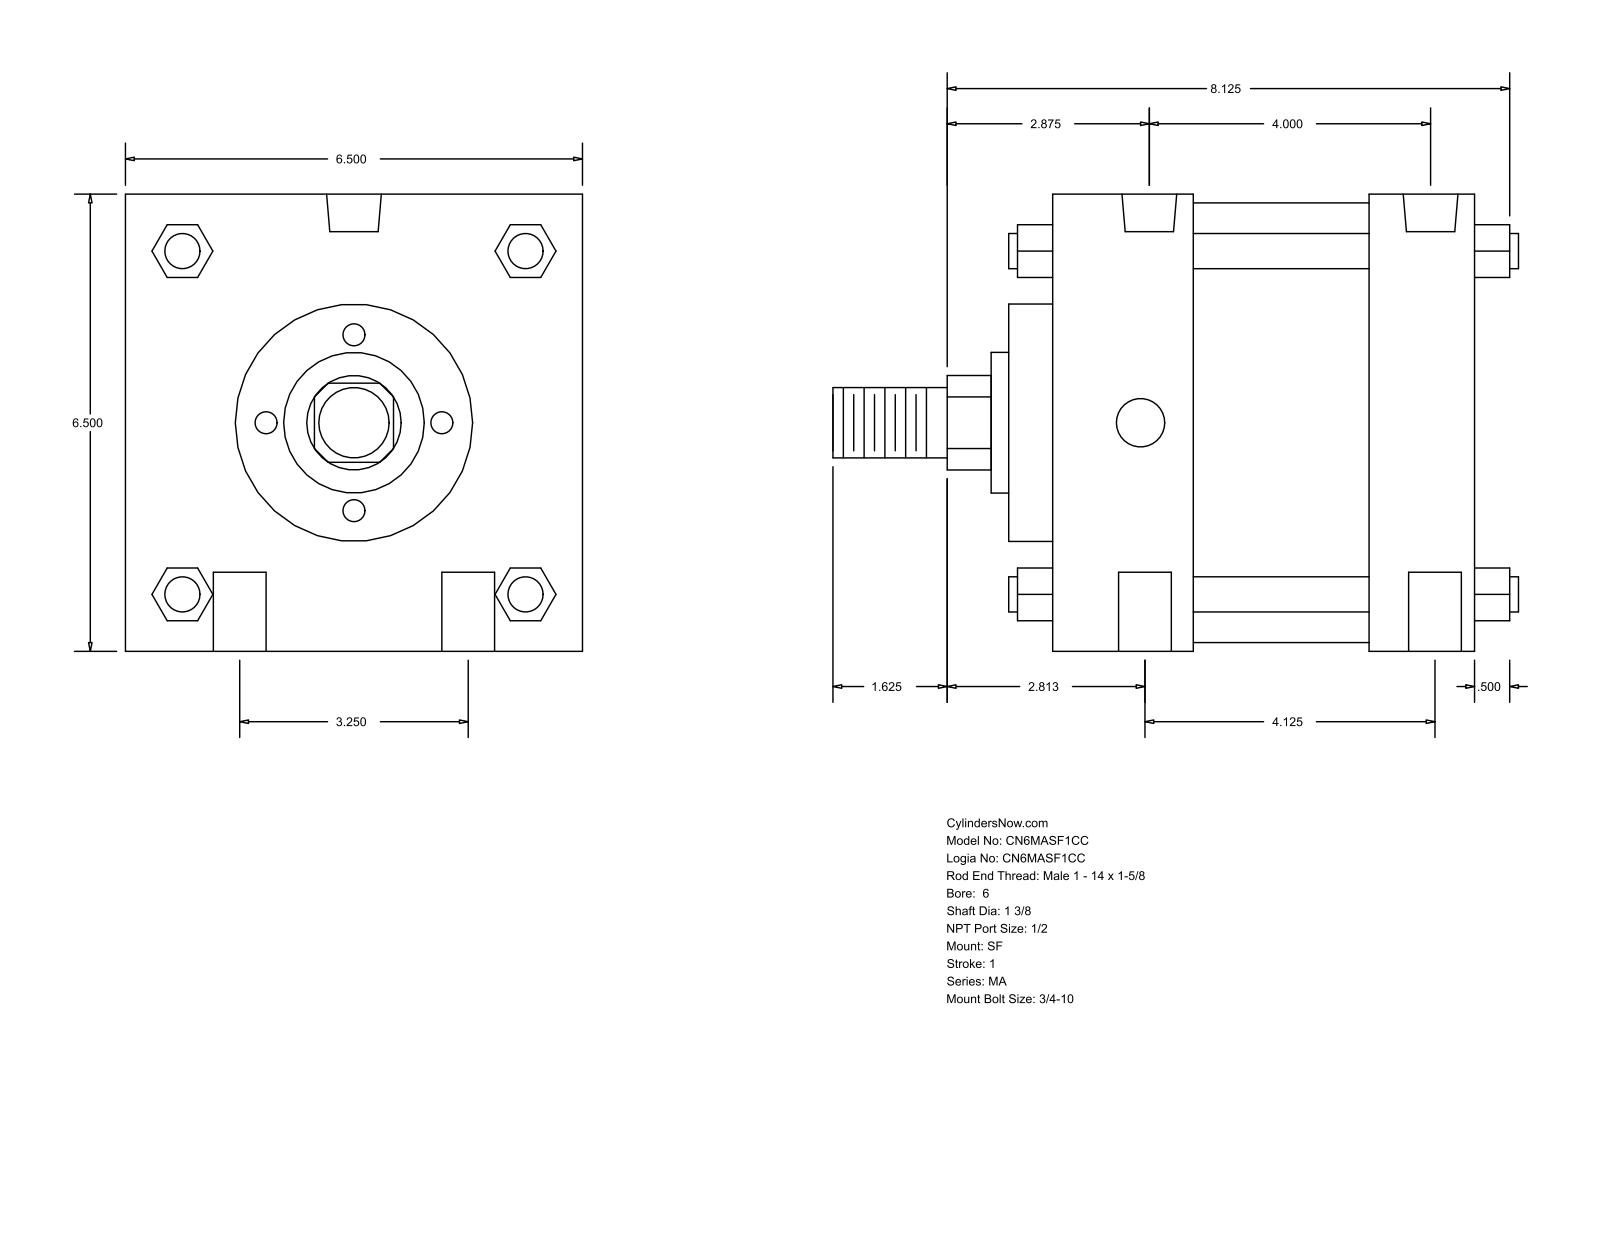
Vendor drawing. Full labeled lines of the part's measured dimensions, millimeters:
Part name (STEP PRODUCT): MA_SF__0600_1.375
STEP written by: GSSL Pune (CONFIG_CONTROL_DESIGN)
Units: millimetres
Bodies: 0 solids, 126 faces (95 planar, 31 cylindrical, 0 other)
Overall size (bounding box): 247.65 × 165.1 × 165.1
Round holes (diameter × count): ⌀19.05 ×4, ⌀17.46 ×2, ⌀19.77 ×2
Round bosses / shafts (diameter × count): ⌀12.7 ×4, ⌀158.75 ×1, ⌀85.72 ×1, ⌀50.8 ×1, ⌀34.92 ×1, ⌀25.4 ×1
Partial cylindrical surfaces — rounded edges, fillets, slot ends (radius × count): R17.06 ×1
Main face-to-face distances: 165.1, 152.4, 63.5, 114.3, 50.8, 38.1, 101.6, 66.67, 130.17, 15.87
Hole centre spacings: 41.3, 111.13, 82.54, 104.77, 133.38, 101.59, 101.6
